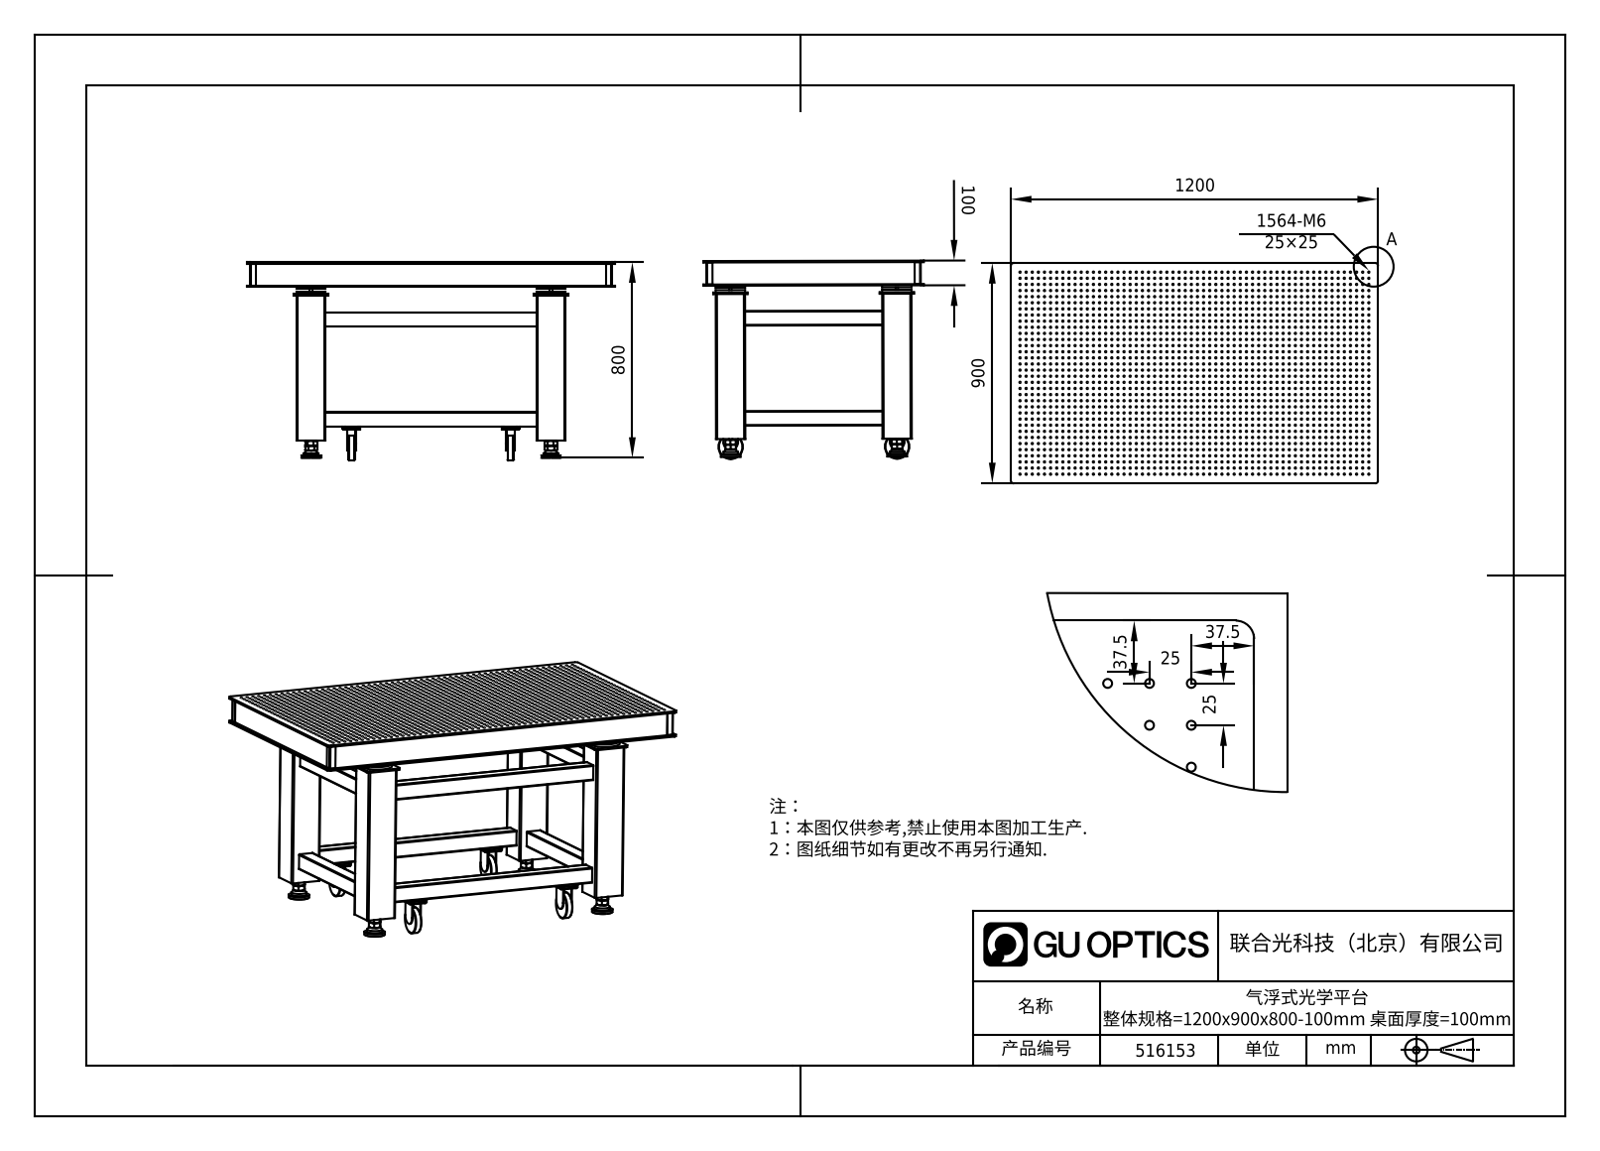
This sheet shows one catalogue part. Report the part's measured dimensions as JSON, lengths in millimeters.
{"part_name": "516153", "step_written_by": "SolidWorks 2020 (CONFIG_CONTROL_DESIGN)", "units": "millimeters", "bodies": {"solids": 62, "faces": 6957, "planar": 2461, "cylindrical": 4304, "other": 192}, "overall_size": [1500, 900, 809], "volume_mm3": 140800000, "surface_area_mm2": 11840000, "round_holes": [[5.3, 1972], [8.5, 16], [9, 16], [17.5, 4], [22, 4], [28, 4], [43, 4]], "round_bosses_or_shafts": [[120, 4], [80, 4], [58, 4], [14, 4], [10, 4], [100, 2]], "partial_cylinders_radius": [[1, 48], [10, 48], [3, 36], [5, 16], [7, 16], [2, 4], [11, 4], [30, 2]], "face_to_face_distances": [5, 96, 101, 2, 58, 4, 116, 680, 980, 28], "hole_center_spacings": [680, 25, 45, 50, 78, 90.05, 147.74, 191.51]}
